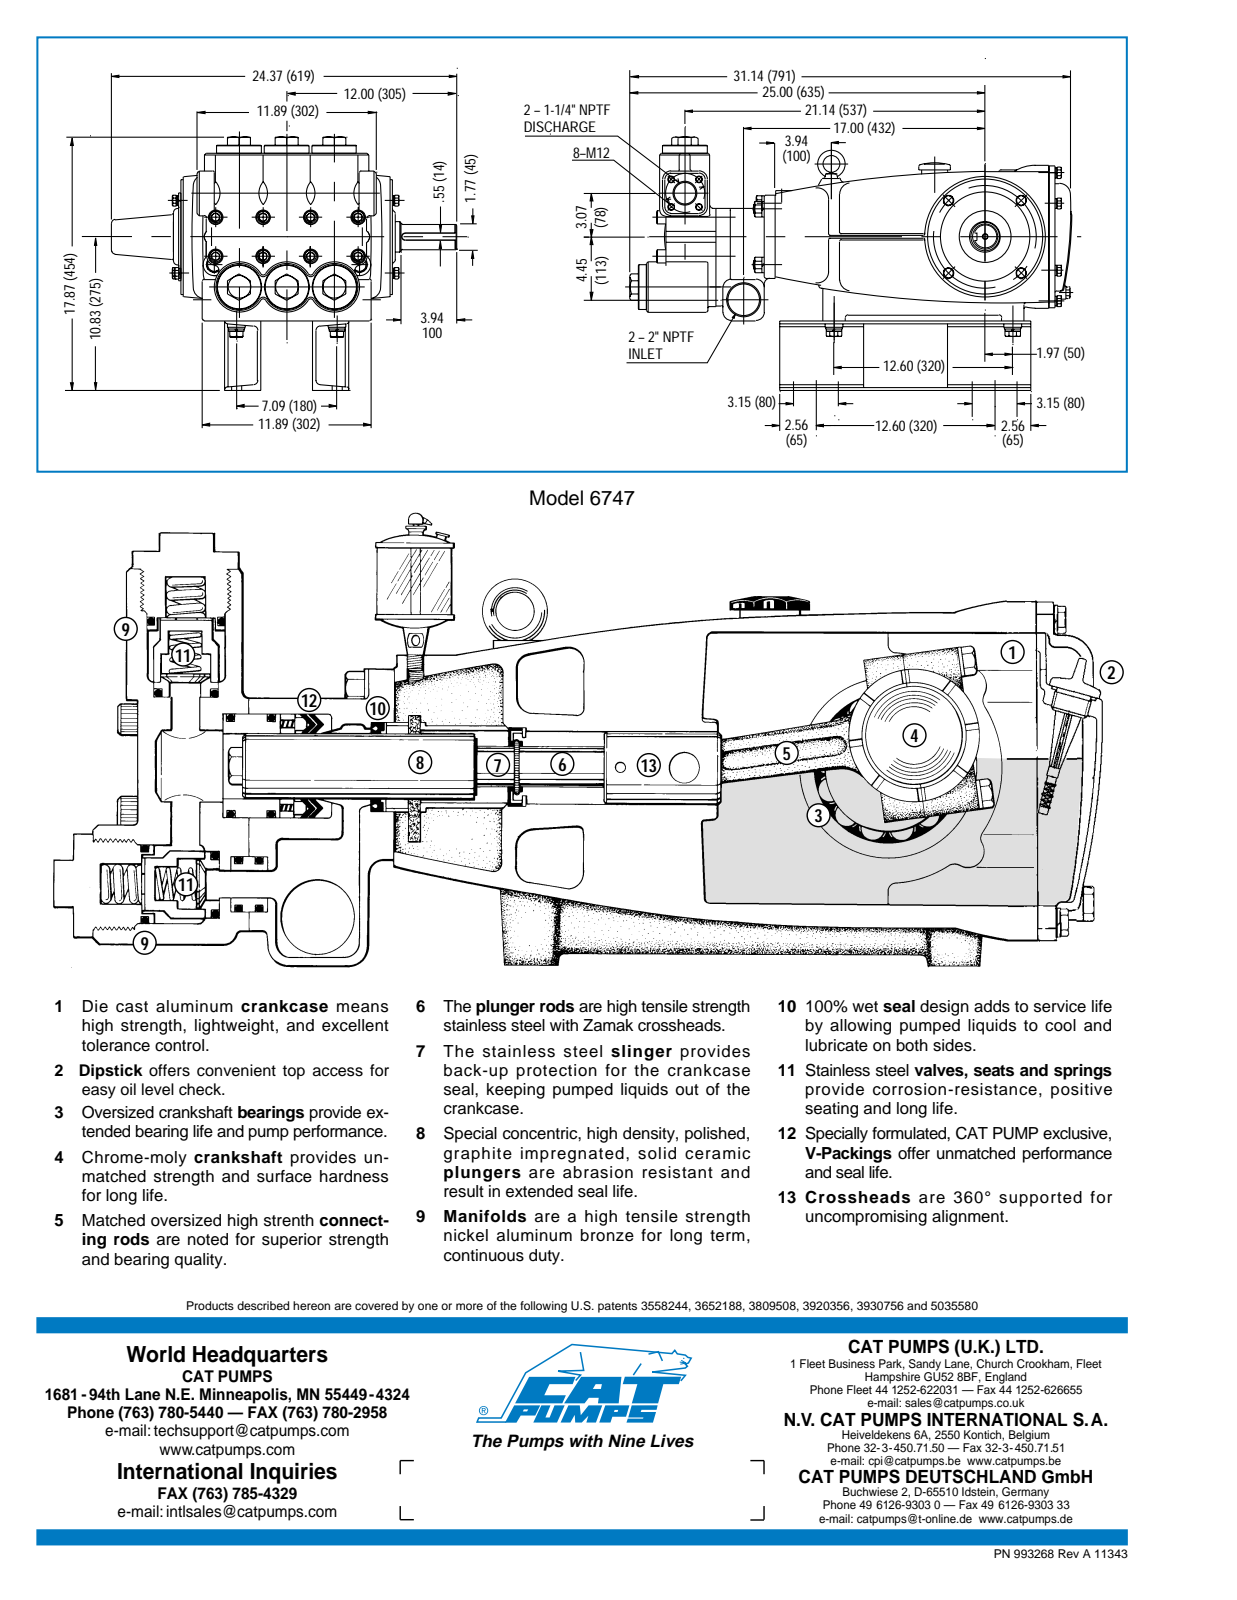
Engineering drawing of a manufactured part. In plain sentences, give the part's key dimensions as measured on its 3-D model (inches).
The part is named "6747". Its 3-D file was written by "SolidWorks 2009 (AUTOMOTIVE_DESIGN)". It is 0 solids with 2046 faces: 594 planar, 611 cylindrical and 841 other. Overall it measures 30.989 by 24.016 by 17.835 inches. Round holes: 7 of diameter 0.551, 4 of diameter 0.406, 2 of diameter 0.315, 2 of diameter 0.394, 2 of diameter 0.413, 1 of diameter 1.496, 1 of diameter 2.213, 1 of diameter 2.835. Round bosses or shafts: 12 of diameter 0.787, 12 of diameter 0.713, 10 of diameter 1.079, 8 of diameter 0.937, 6 of diameter 3.15, 4 of diameter 1.181, 2 of diameter 1.102, 2 of diameter 0.63. Partial cylindrical surfaces (rounded edges, fillets, slot ends): 56 of radius 0.118, 37 of radius 0.079, 33 of radius 0.197, 26 of radius 0.394, 21 of radius 0.787, 13 of radius 0.157, 12 of radius 0.354, 12 of radius 0.591. The main face-to-face distances are 3.78, 4.921, 0.236, 4.173, 0.394, 3.543, 9.449, 5.433, 9.055, 9.213. The hole center spacings are 1.392, 1.463, 1.969, 10.621, 3.346, 2.756, 2.784, 3.846.
